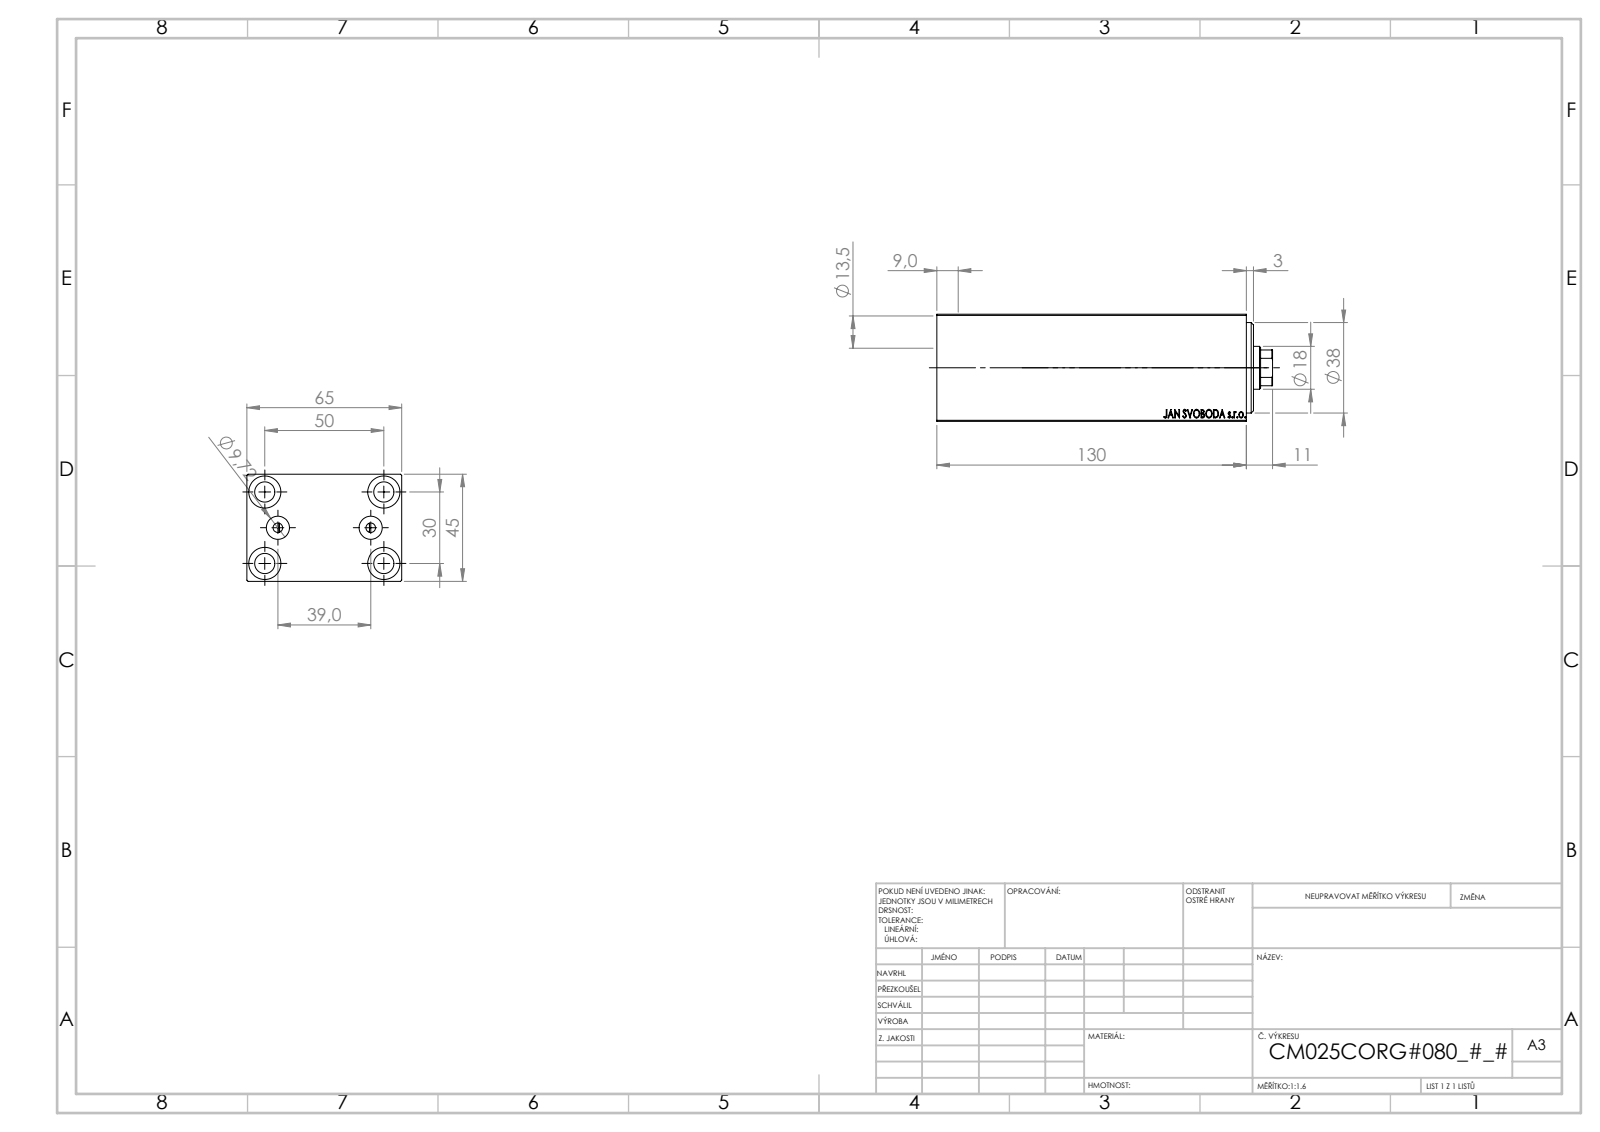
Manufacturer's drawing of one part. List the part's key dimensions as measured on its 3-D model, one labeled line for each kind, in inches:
Part name (STEP PRODUCT): V450CM_VC_B; V450CM_C_Body; V450CM_C_VCP
STEP written by: SolidWorks 2019 (CONFIG_CONTROL_DESIGN)
Units: inches
Bodies: 3 solids, 858 faces (408 planar, 56 cylindrical, 394 other)
Overall size (bounding box): 5.551 × 2.559 × 1.772
Volume: 19.84 in³ · Surface area: 117.9 in²
Round holes (diameter × count): ⌀0.335 ×5, ⌀0.531 ×4, ⌀0.157 ×2, ⌀0.383 ×2, ⌀0.709 ×1, ⌀0.846 ×1, ⌀0.984 ×1, ⌀1.063 ×1, ⌀1.496 ×1
Partial cylindrical surfaces — rounded edges, fillets, slot ends (radius × count): R0.335 ×1
Main face-to-face distances: 1.772, 2.559, 0.236, 4.685, 4.882, 4.921, 0.197, 5.118, 0.118, 0.315
Hole centre spacings: 0.629, 1.148, 1.849, 0.768, 1.181, 1.969, 2.296, 1.535
